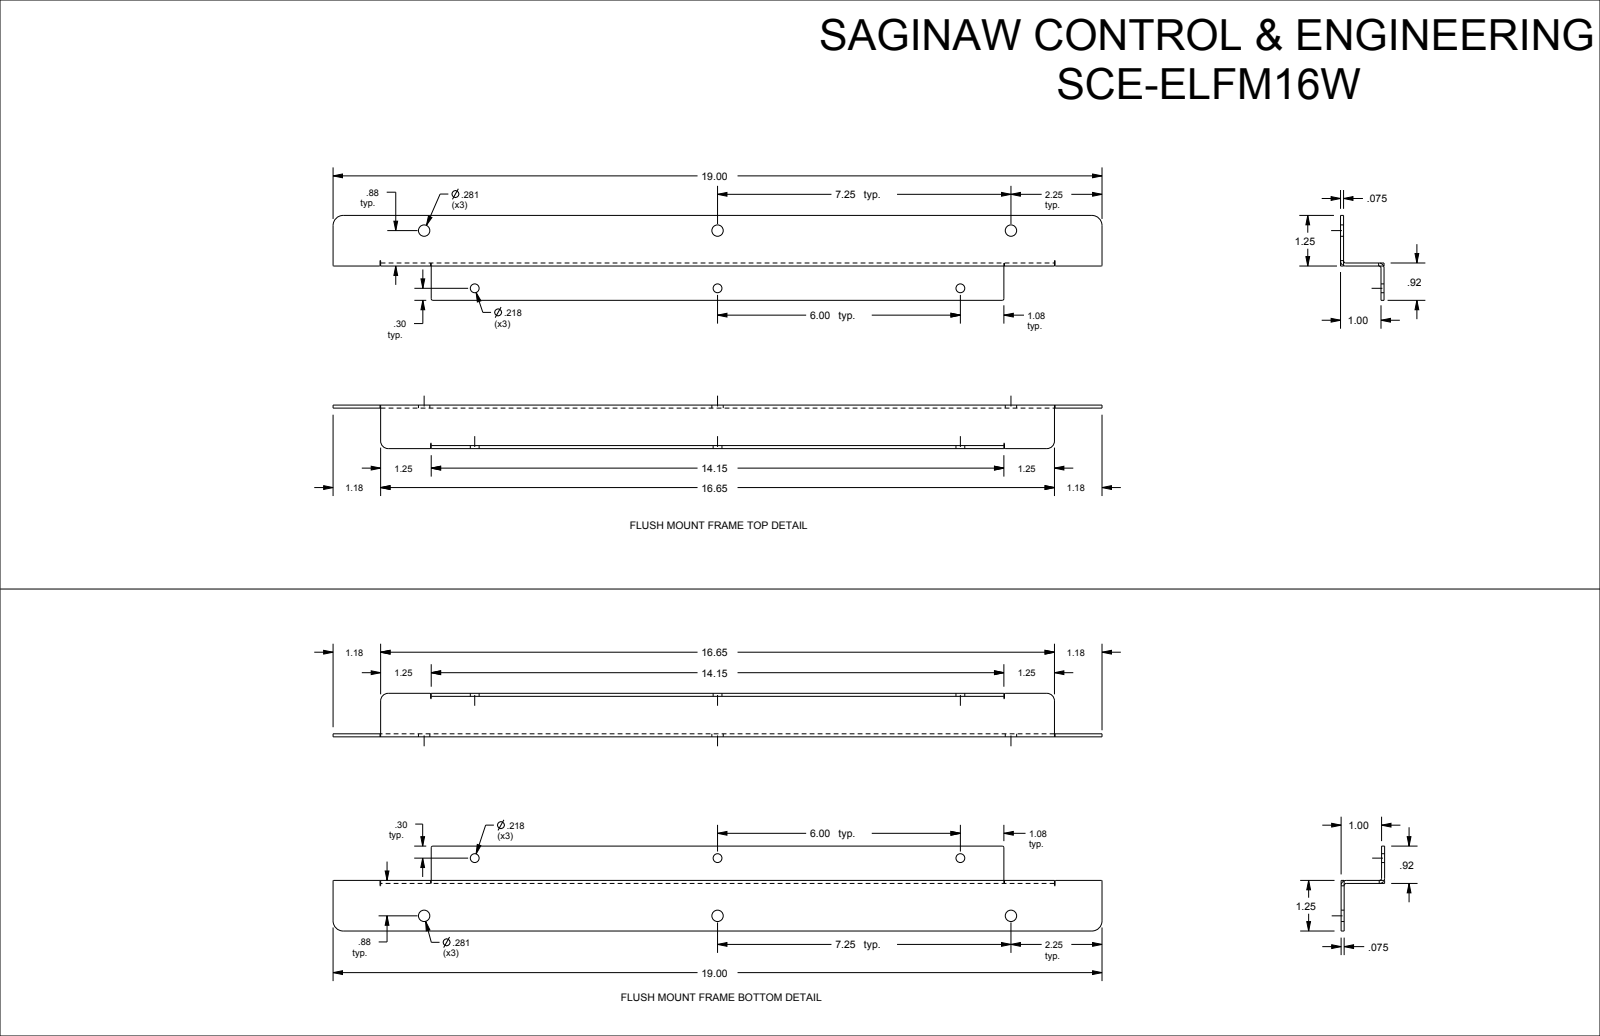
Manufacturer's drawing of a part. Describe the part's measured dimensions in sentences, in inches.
The part is named "SCE-ELFM16W". Its 3-D file was written by "SolidWorks 2019 (CONFIG_CONTROL_DESIGN)". It is 2 solids with 96 faces: 44 planar, 52 cylindrical and 0 other. Overall it measures 19 by 18.35 by 1.075 inches. Its volume is 7.63 cubic inches and its surface area 210.9 square inches. Round holes: 6 of diameter 0.218, 6 of diameter 0.281. Partial cylindrical surfaces (rounded edges, fillets, slot ends): 10 of radius 0.015, 4 of radius 0.008, 4 of radius 0.04, 4 of radius 0.051, 4 of radius 0.126, 4 of radius 0.25, 2 of radius 0.007, 2 of radius 0.187. The main face-to-face distances are 0.075, 1, 0.075, 15.925, 1.075, 0.925, 15.85, 16, 1.175, 1.25. The hole center spacings are 1.895, 6, 6.167, 7.25, 7.389, 13.326, 15.924, 16.223.
